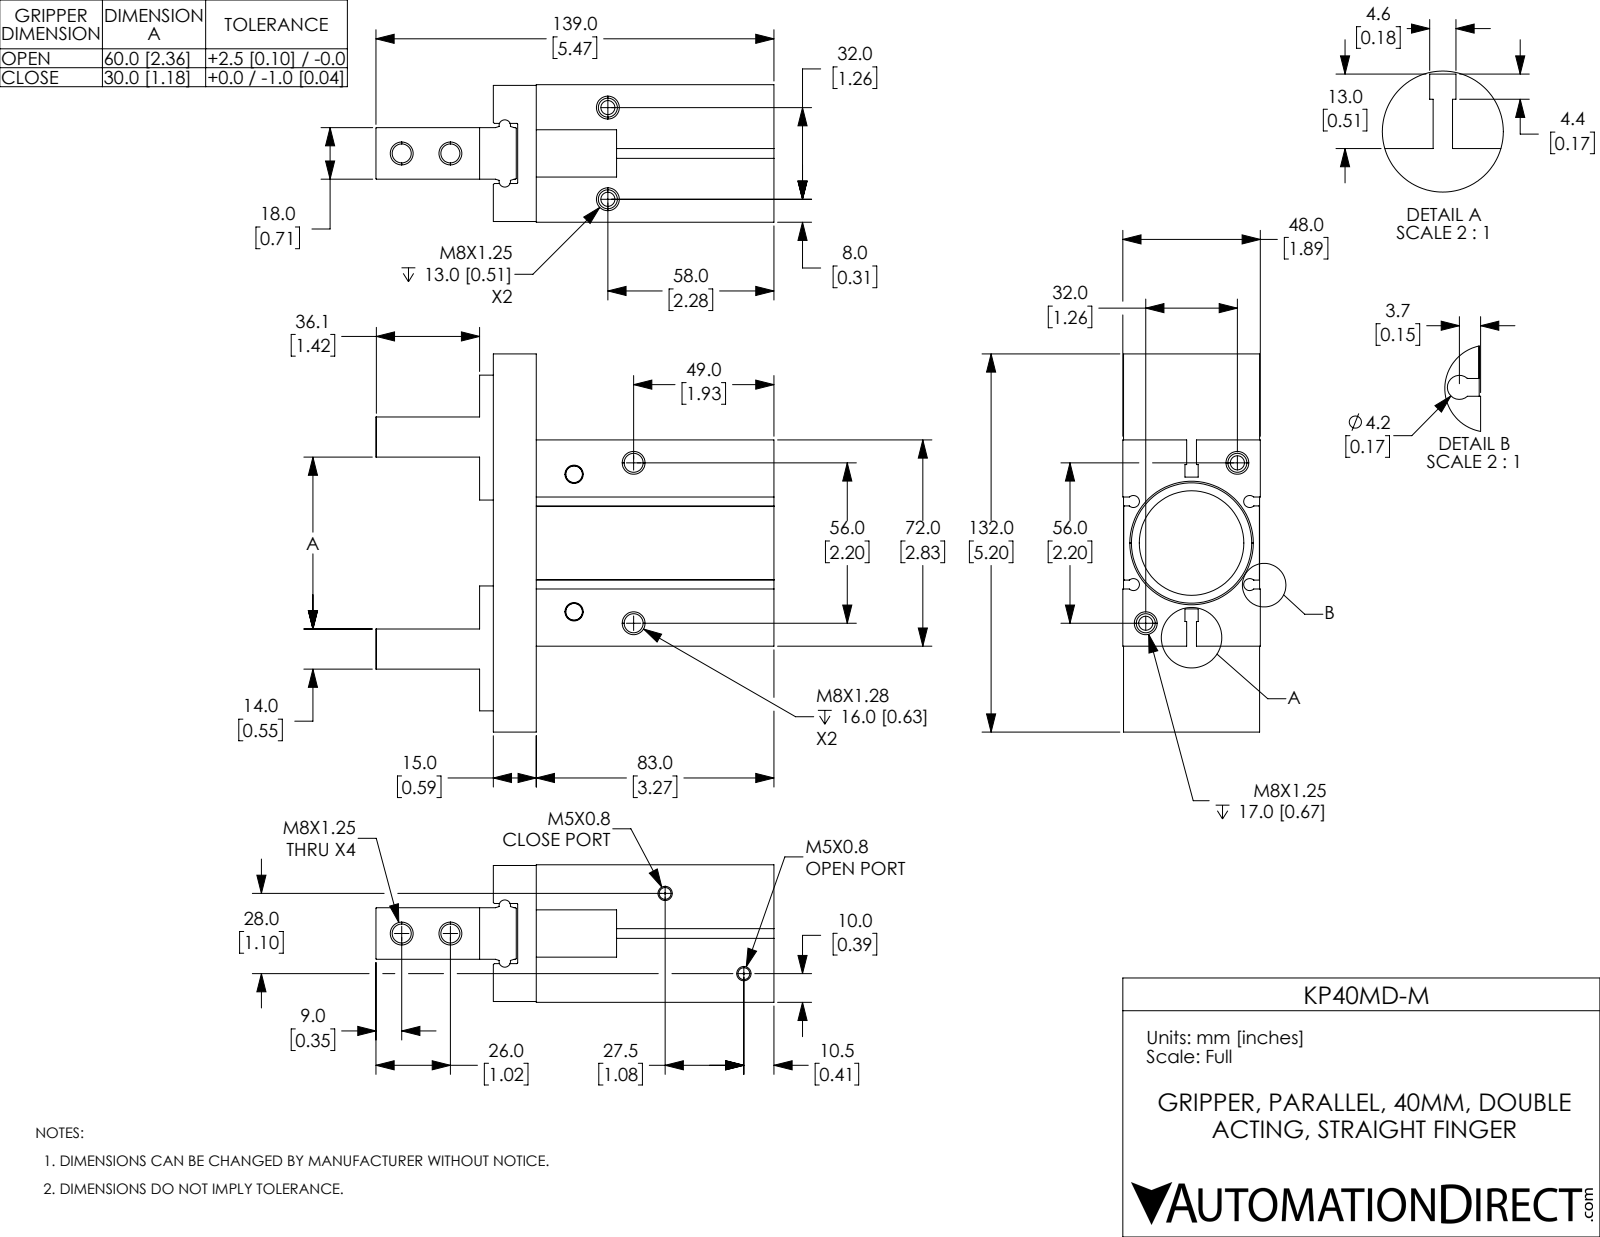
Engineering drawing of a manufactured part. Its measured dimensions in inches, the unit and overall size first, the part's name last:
Units: inches
Overall size (bounding box): 5.472 × 5.197 × 1.89
Round holes (diameter × count): ⌀0.262 ×7, ⌀0.02 ×2, ⌀0.163 ×2, ⌀0.316 ×2, ⌀0.262 ×1, ⌀1.437 ×1, ⌀1.654 ×1
Partial cylindrical surfaces — rounded edges, fillets, slot ends (radius × count): R0.008 ×7, R0.083 ×4, R0.012 ×2, R0.079 ×2
Main face-to-face distances: 0.591, 1.878, 0.62, 1.27, 0.608, 1.258, 1.88, 0.61, 1.26, 1.868
Hole centre spacings: 1.27, 2.255, 2.904, 0.669, 0.791, 1.26, 1.42, 1.545
Volume: 20.53 in³ · Surface area: 105.1 in²
Bodies: 3 solids, 243 faces (118 planar, 63 cylindrical, 62 other)
Part name (STEP PRODUCT): KP40MD-M-1; KP40MD-M-2; KP40MD-M-3; KP40MD-M
STEP written by: SolidWorks 2017 (CONFIG_CONTROL_DESIGN)
